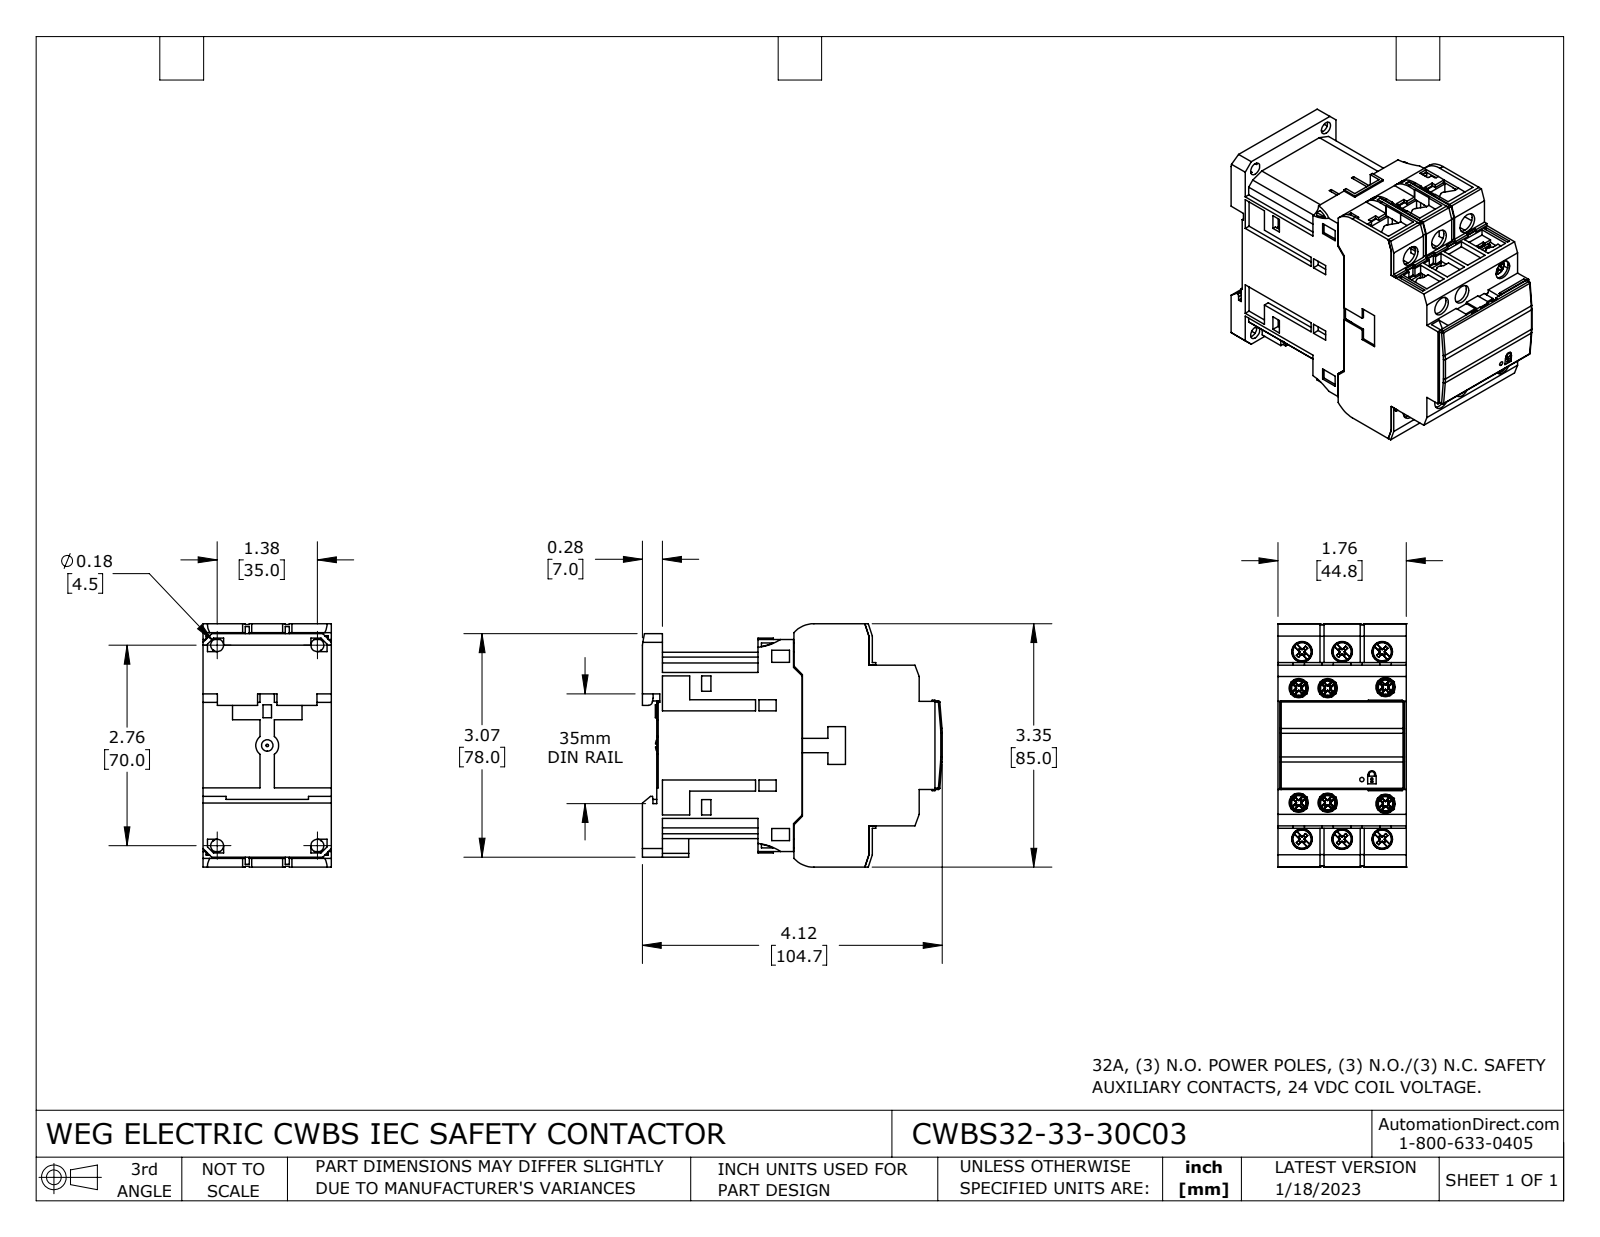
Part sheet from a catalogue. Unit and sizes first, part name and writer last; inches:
Units: inches
Overall size (bounding box): 4.122 × 3.346 × 1.764
Round holes (diameter × count): ⌀0.124 ×6, ⌀0.142 ×6, ⌀0.264 ×6, ⌀0.283 ×6, ⌀0.177 ×4, ⌀0.236 ×2, ⌀0.059 ×1
Round bosses / shafts (diameter × count): ⌀0.201 ×6, ⌀0.169 ×6, ⌀0.157 ×6, ⌀0.138 ×6, ⌀0.107 ×6
Partial cylindrical surfaces — rounded edges, fillets, slot ends (radius × count): R0.008 ×72, R0.012 ×54, R0.004 ×48, R0.02 ×37, R0.028 ×24, R0.071 ×12, R0.081 ×12, R0.964 ×12
Main face-to-face distances: 1.764, 0.047, 1.823, 1.827, 0.024, 0.272, 0.646, 0.217, 3.807, 0.094
Hole centre spacings: 0.165, 0.551, 0.664, 0.695, 0.829, 1.243, 2.272, 2.396
Volume: 16.15 in³ · Surface area: 115.3 in²
Bodies: 42 solids, 3062 faces (1894 planar, 647 cylindrical, 521 other)
Part name (STEP PRODUCT): CWBS32-33-30C03
STEP written by: SolidWorks 2021 (CONFIG_CONTROL_DESIGN)
